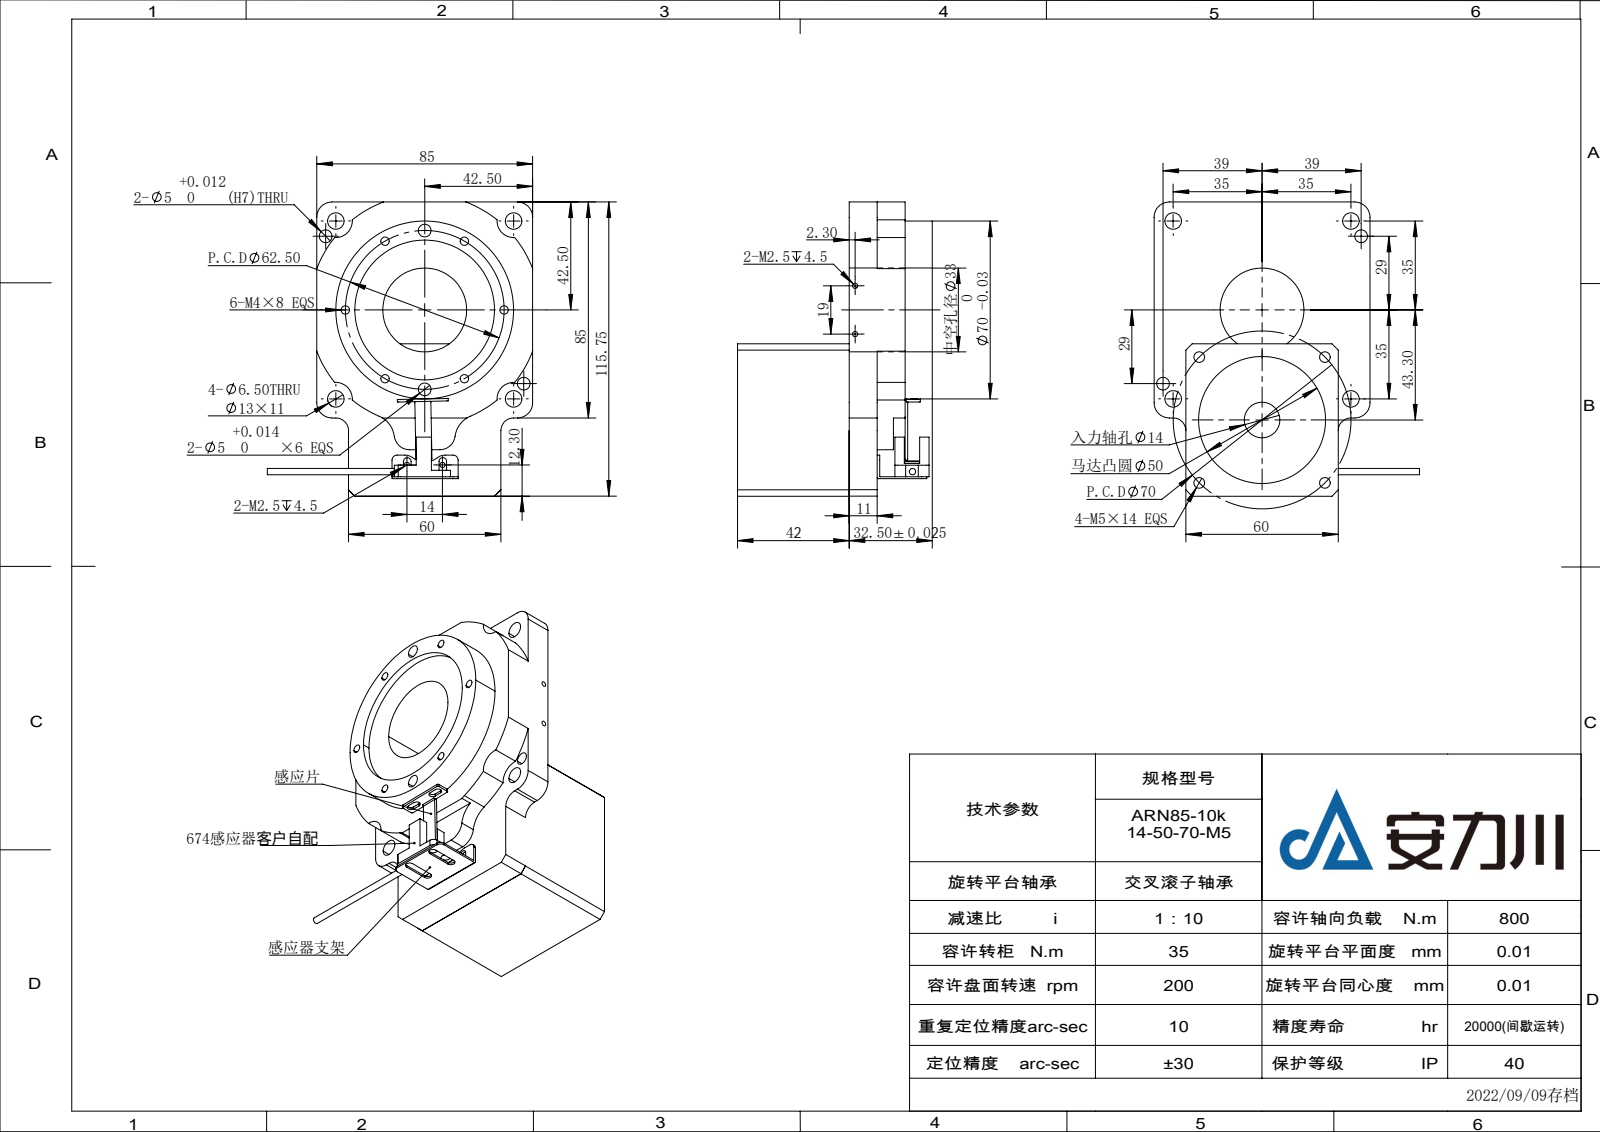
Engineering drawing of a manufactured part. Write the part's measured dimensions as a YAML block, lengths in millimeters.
part_name: "KTN85-10K-14-50-70-M4(总高74.5); KTN85-10K-14-50-70-M4; SX674; 感应片1 (+1 more)"
step_written_by: "SolidWorks 2020 (AUTOMOTIVE_DESIGN)"
units: millimeters
bodies: {solids: 4, faces: 283, planar: 117, cylindrical: 126, other: 40}
overall_size: [115.8, 104.39, 74.5]
volume: 313038
surface_area: 48023
round_holes:
  - {diameter: 3.3, count: 10}
  - {diameter: 2.05, count: 6}
  - {diameter: 5, count: 4}
  - {diameter: 6.5, count: 4}
  - {diameter: 3.5, count: 2}
  - {diameter: 14, count: 1}
  - {diameter: 33, count: 1}
  - {diameter: 50, count: 1}
  - {diameter: 55, count: 1}
round_bosses_or_shafts:
  - {diameter: 70, count: 1}
  - {diameter: 2.5, count: 1}
partial_cylinders:
  - {radius: 0.5, count: 9}
  - {radius: 1.5, count: 8}
  - {radius: 2, count: 6}
  - {radius: 6, count: 6}
  - {radius: 1.65, count: 4}
  - {radius: 5, count: 4}
  - {radius: 6.5, count: 4}
  - {radius: 1, count: 2}
face_to_face_distances: [11, 60, 22, 12.5, 72.5, 37, 48, 59, 5, 42]
hole_center_spacings: [31.25, 35.2, 49.5, 74.93, 70, 31.24, 35, 44.19]
